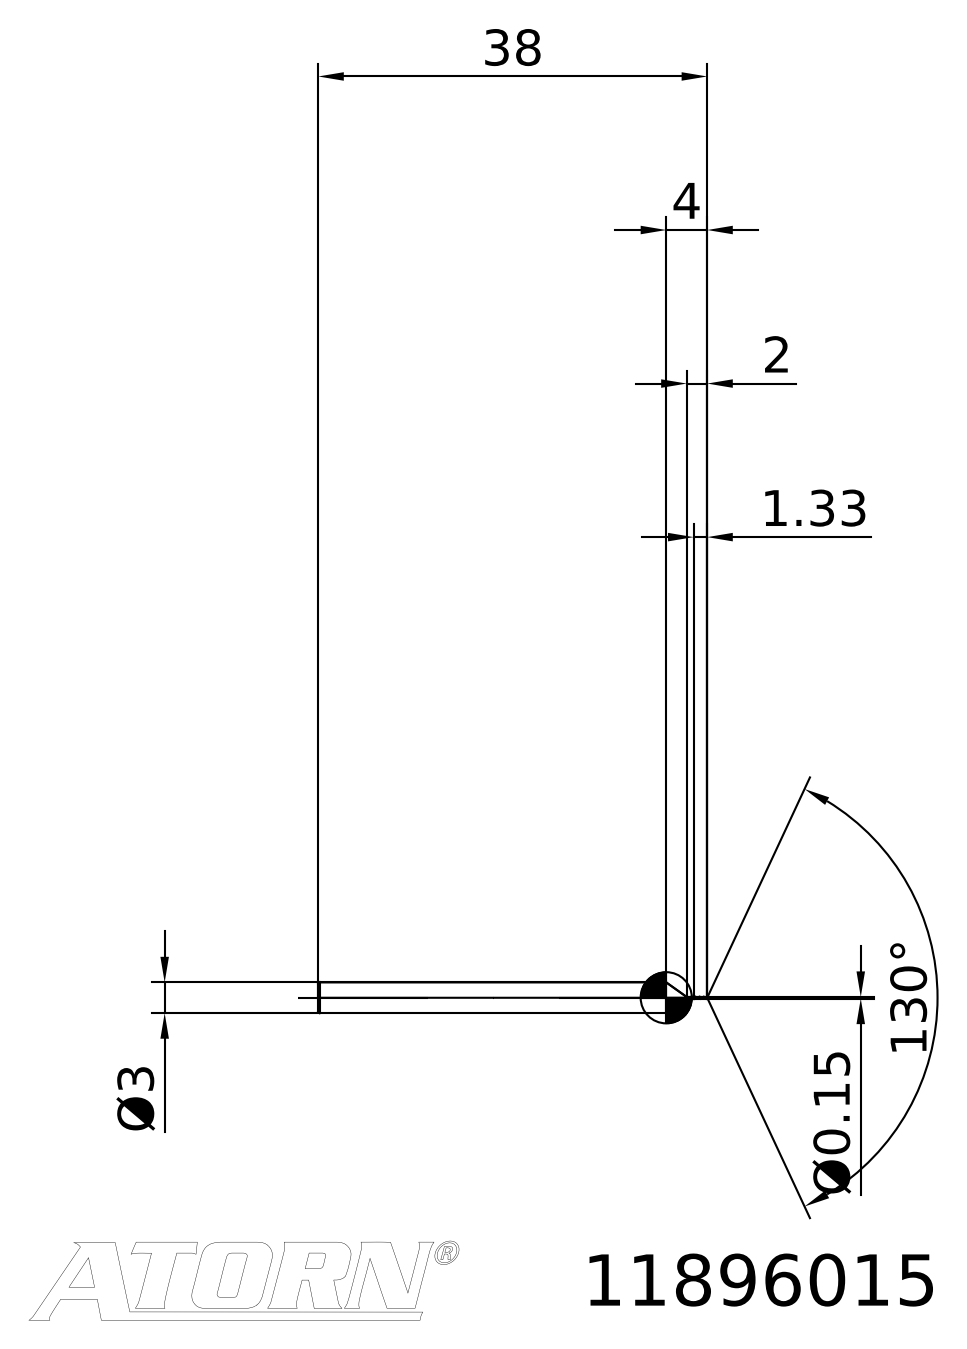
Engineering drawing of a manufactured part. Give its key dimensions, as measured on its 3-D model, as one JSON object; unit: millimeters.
{"step_written_by": "TDM (AUTOMOTIVE_DESIGN)", "units": "millimeters", "bodies": {"solids": 2, "faces": 30, "planar": 3, "cylindrical": 0, "other": 27}, "overall_size": [38, 3, 3], "volume_mm3": 245, "surface_area_mm2": 340, "face_to_face_distances": [36.67]}
